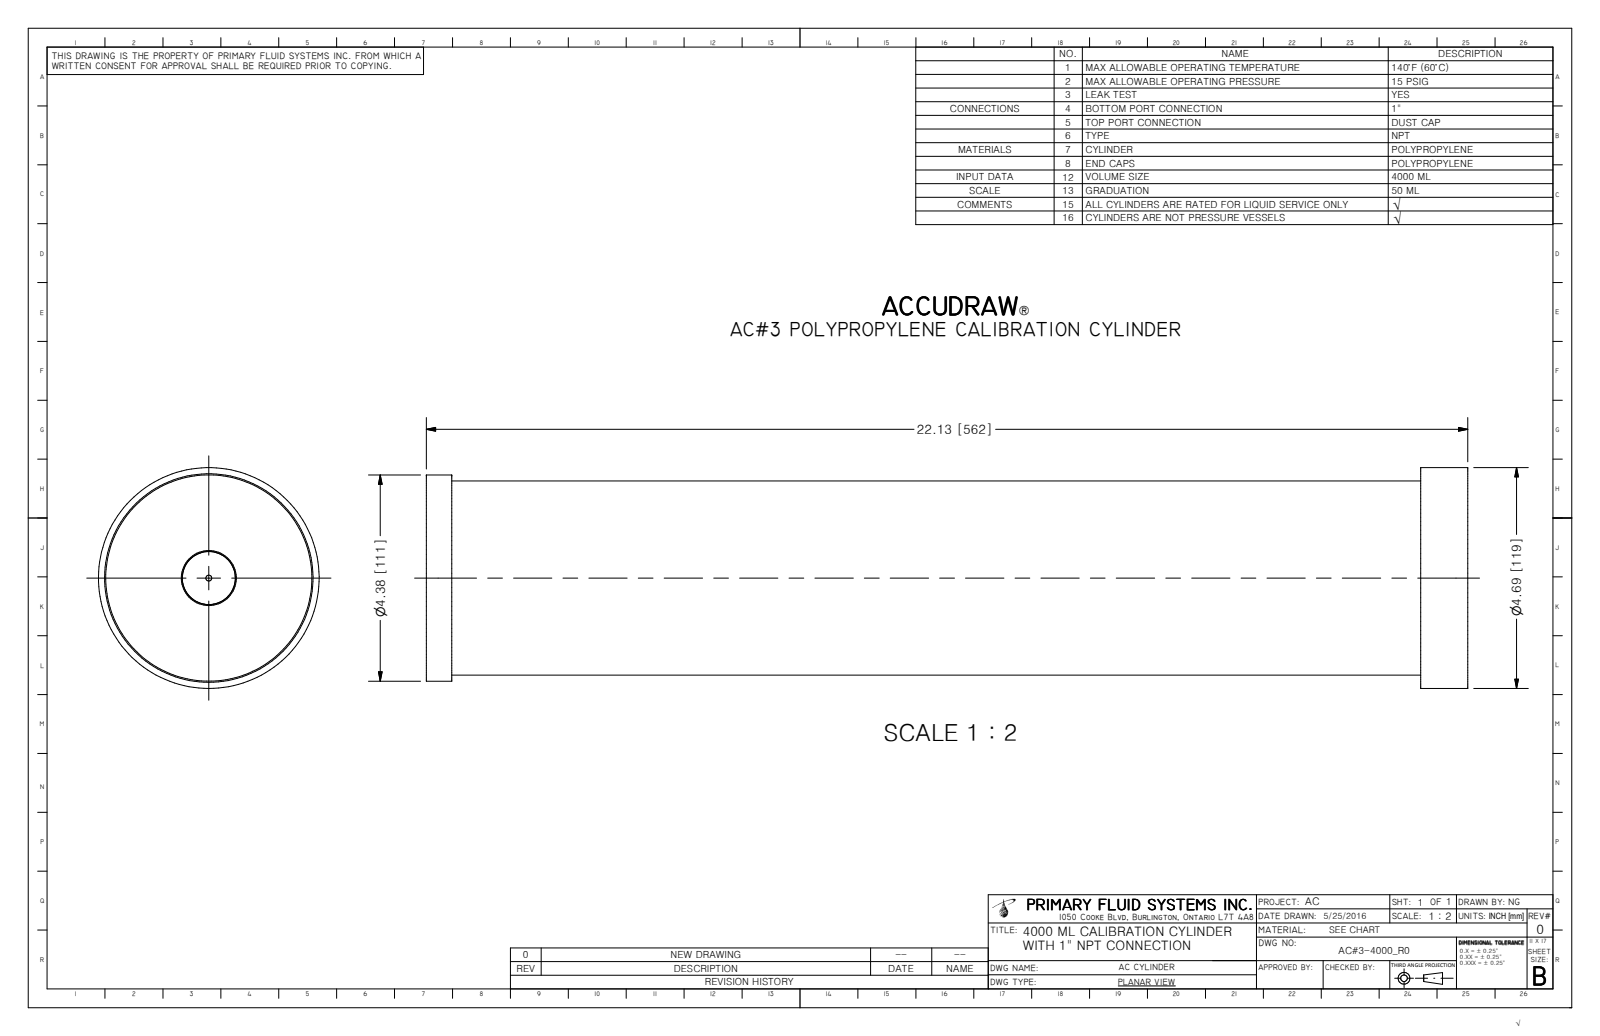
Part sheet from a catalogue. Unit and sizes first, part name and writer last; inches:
Units: inches
Overall size (bounding box): 22.13 × 4.69 × 4.69
Round holes (diameter × count): ⌀0.125 ×1, ⌀4.005 ×1, ⌀4.43 ×1
Round bosses / shafts (diameter × count): ⌀4.69 ×1, ⌀4.38 ×1, ⌀4.125 ×1, ⌀4.115 ×1, ⌀3.95 ×1
Main face-to-face distances: 1, 21.13, 22.13, 0.75, 20.38, 21.38, 0.5, 0.54, 0.21, 20.59
Volume: 42.27 in³ · Surface area: 643.1 in²
Bodies: 3 solids, 20 faces (9 planar, 8 cylindrical, 3 other)
Part name (STEP PRODUCT): AC#3-4000_R0; AC-2B-4000; AC-4000-TUBE; AC-DC-4000_R1
STEP written by: Autodesk Inventor 2009 (AUTOMOTIVE_DESIGN)
